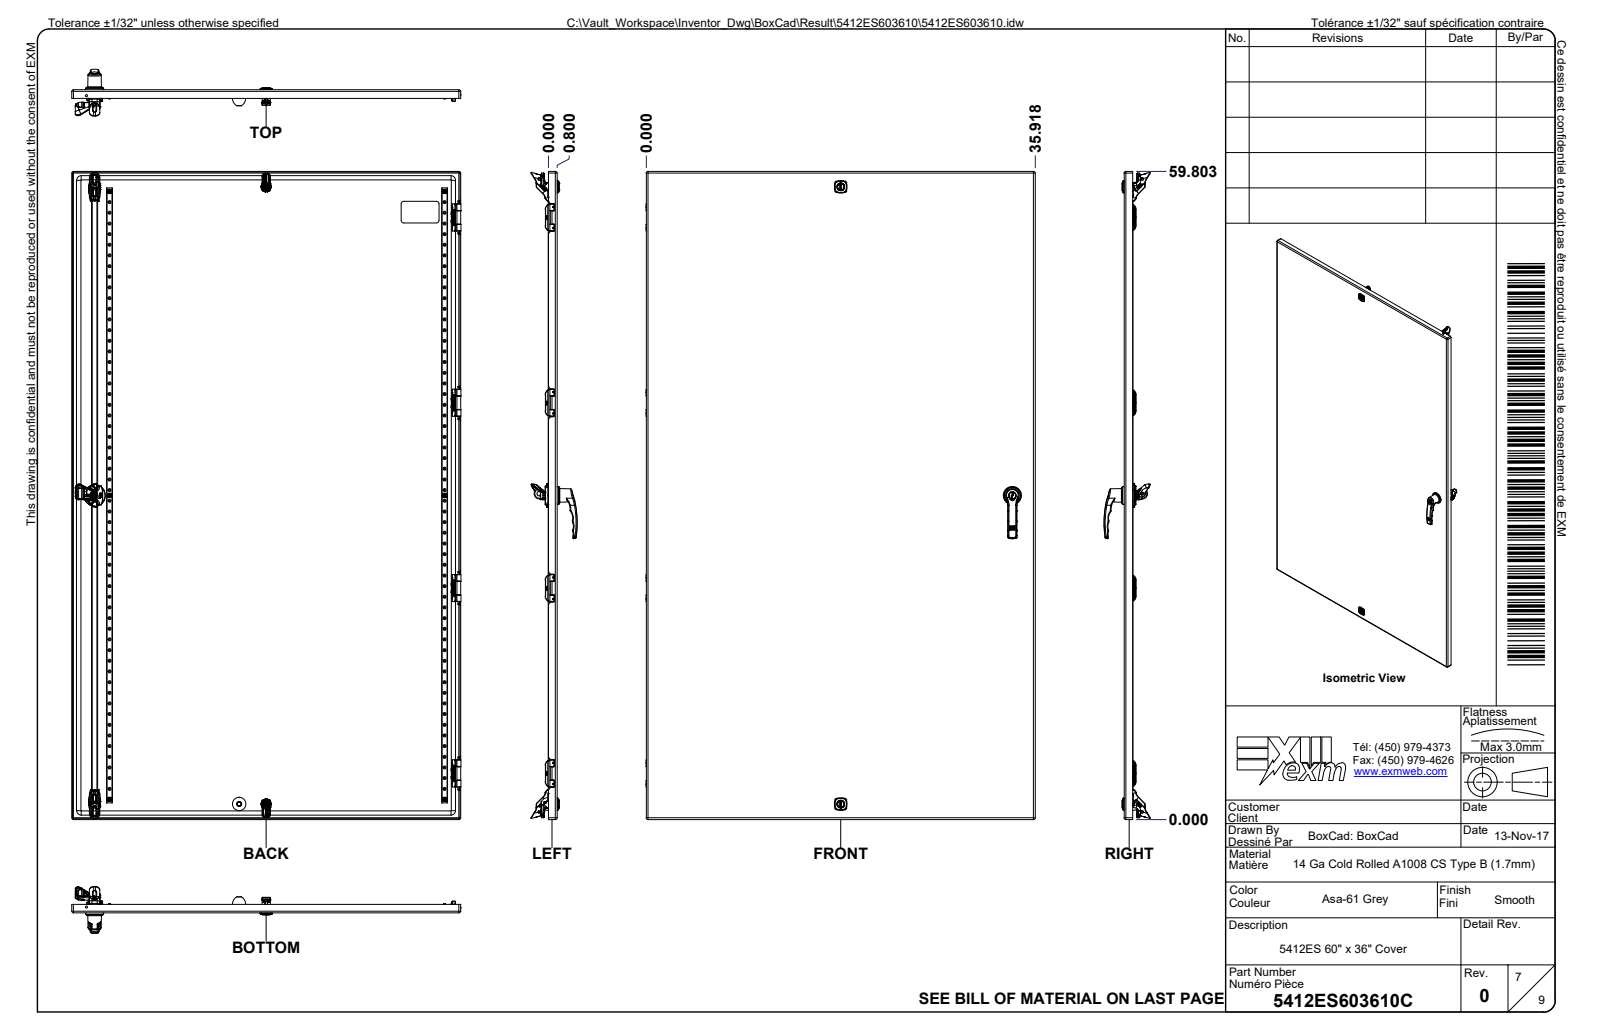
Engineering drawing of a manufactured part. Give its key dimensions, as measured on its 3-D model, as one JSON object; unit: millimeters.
{"part_name": "5412ES603610; 5412ES603610B; 5412ES603610B-P; STK-Q-16005 (+8 more)", "step_written_by": "Autodesk Inventor 2024 (AUTOMOTIVE_DESIGN)", "units": "millimeters", "bodies": {"solids": 123, "faces": 21783, "planar": 6232, "cylindrical": 5367, "other": 10184}, "overall_size": [1524, 914.9, 329.8], "volume_mm3": 11620000, "surface_area_mm2": 11960000, "round_holes": [[4.2, 112], [0.8, 18], [1.1, 16], [8, 14], [5.1, 13], [7.9, 11], [4.5, 8], [6.9, 8], [5, 6], [6.8, 6], [12.7, 5], [4.7, 4]], "round_bosses_or_shafts": [[6, 112], [0.8, 18], [1, 16], [5.9, 15], [18.2, 8], [7.9, 8], [6.7, 8], [4.5, 7]], "partial_cylinders_radius": [[0.5, 458], [0.3, 340], [1, 308], [0.2, 168], [0.4, 58], [2, 56], [0.3, 48], [1.5, 46]], "face_to_face_distances": [1.7, 280.7, 279, 282.4, 23.9, 22.2, 256.8, 258.5, 26.6, 24.9], "hole_center_spacings": [434.4, 868.7, 8.9, 18.7, 26.7, 35.2, 50, 434.4]}
